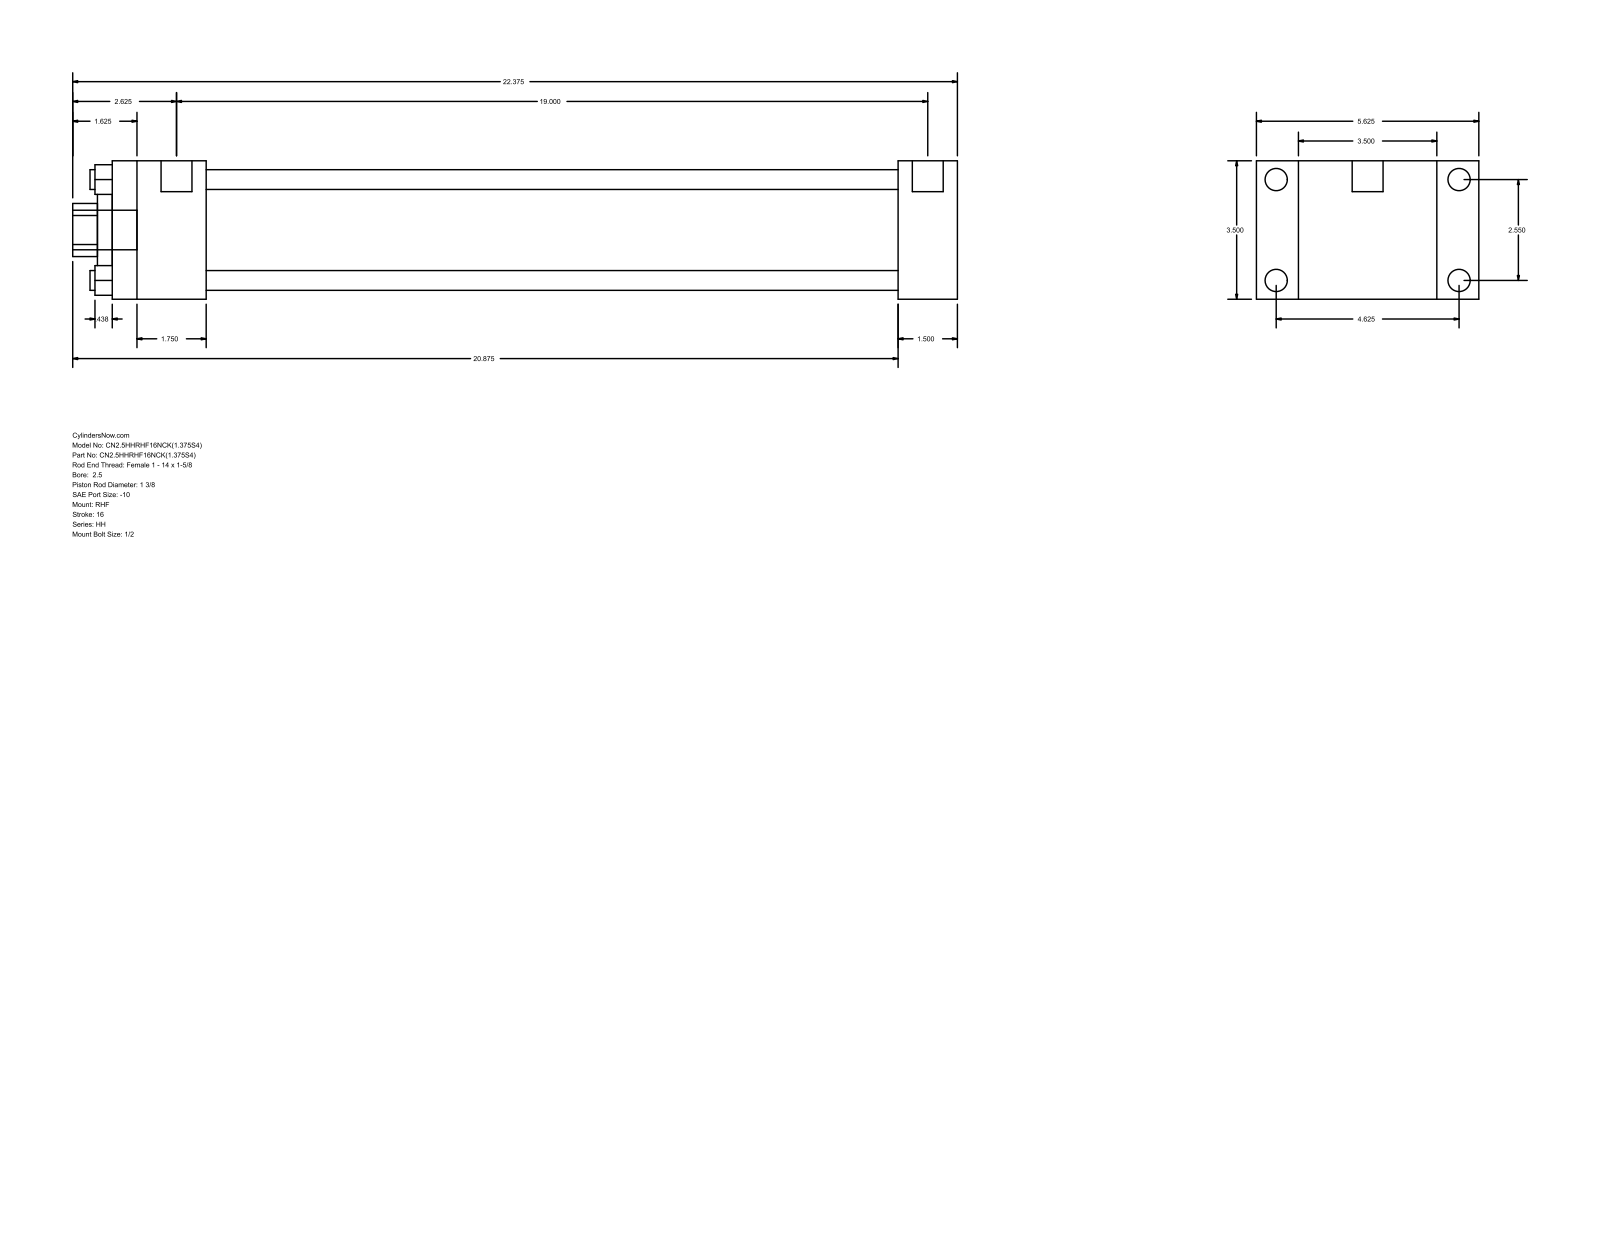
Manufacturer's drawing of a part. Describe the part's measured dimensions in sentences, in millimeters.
The part is named "HH_RHF__0250_1.375". Its 3-D file was written by "GSSL Pune (CONFIG_CONTROL_DESIGN)". It is 0 solids with 88 faces: 60 planar, 28 cylindrical and 0 other. Overall it measures 568.33 by 142.88 by 88.9 millimeters. Round holes: 4 of diameter 12.7, 1 of diameter 34.92, 1 of diameter 50.8, 1 of diameter 73.03. Round bosses or shafts: 4 of diameter 14.3, 4 of diameter 5.56, 2 of diameter 19.84, 1 of diameter 25.4. Partial cylindrical surfaces (rounded edges, fillets, slot ends): 1 of radius 17.06. The main face-to-face distances are 88.9, 38.1, 26.99, 115.89, 504.83, 542.93, 142.88, 60.32, 444.51, 482.61. The hole center spacings are 45.79, 64.76, 91.58.
